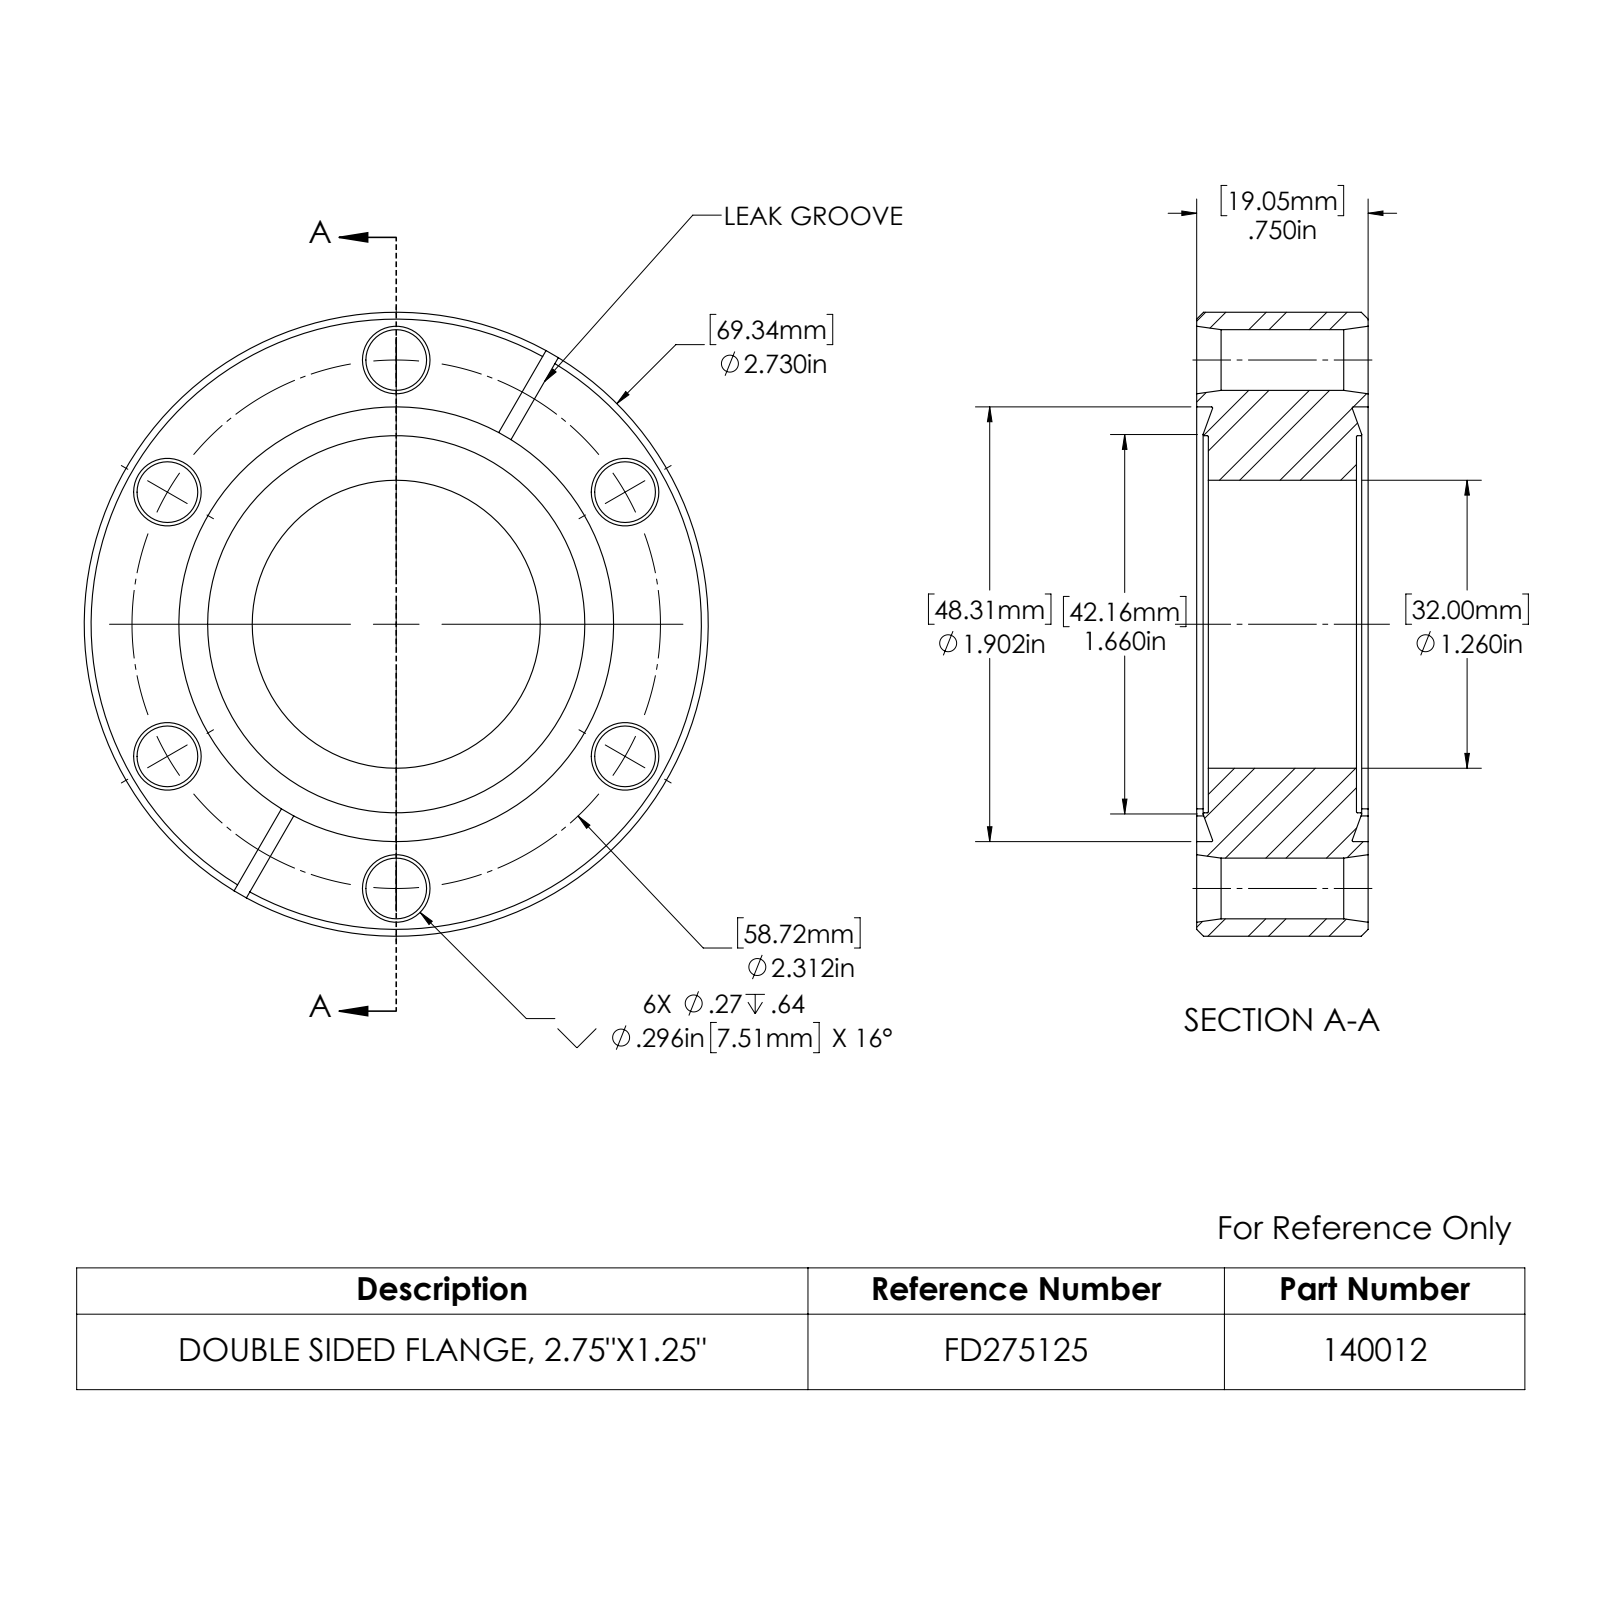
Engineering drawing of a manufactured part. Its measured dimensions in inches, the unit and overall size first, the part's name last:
Units: inches
Overall size (bounding box): 2.73 × 2.73 × 0.75
Round holes (diameter × count): ⌀0.266 ×6, ⌀1.26 ×1, ⌀1.65 ×1, ⌀1.902 ×1
Round bosses / shafts (diameter × count): ⌀2.73 ×1
Partial cylindrical surfaces — rounded edges, fillets, slot ends (radius × count): R1.25 ×4
Main face-to-face distances: 0.75, 0.051, 0.699, 0.648, 0.062
Hole centre spacings: 1.156, 2.002, 2.002, 2.312, 2.312
Volume: 3.018 in³ · Surface area: 22.31 in²
Bodies: 1 solid, 88 faces (14 planar, 28 cylindrical, 46 other)
Part name (STEP PRODUCT): 140012_A
STEP written by: SolidWorks 2022 (CONFIG_CONTROL_DESIGN)
